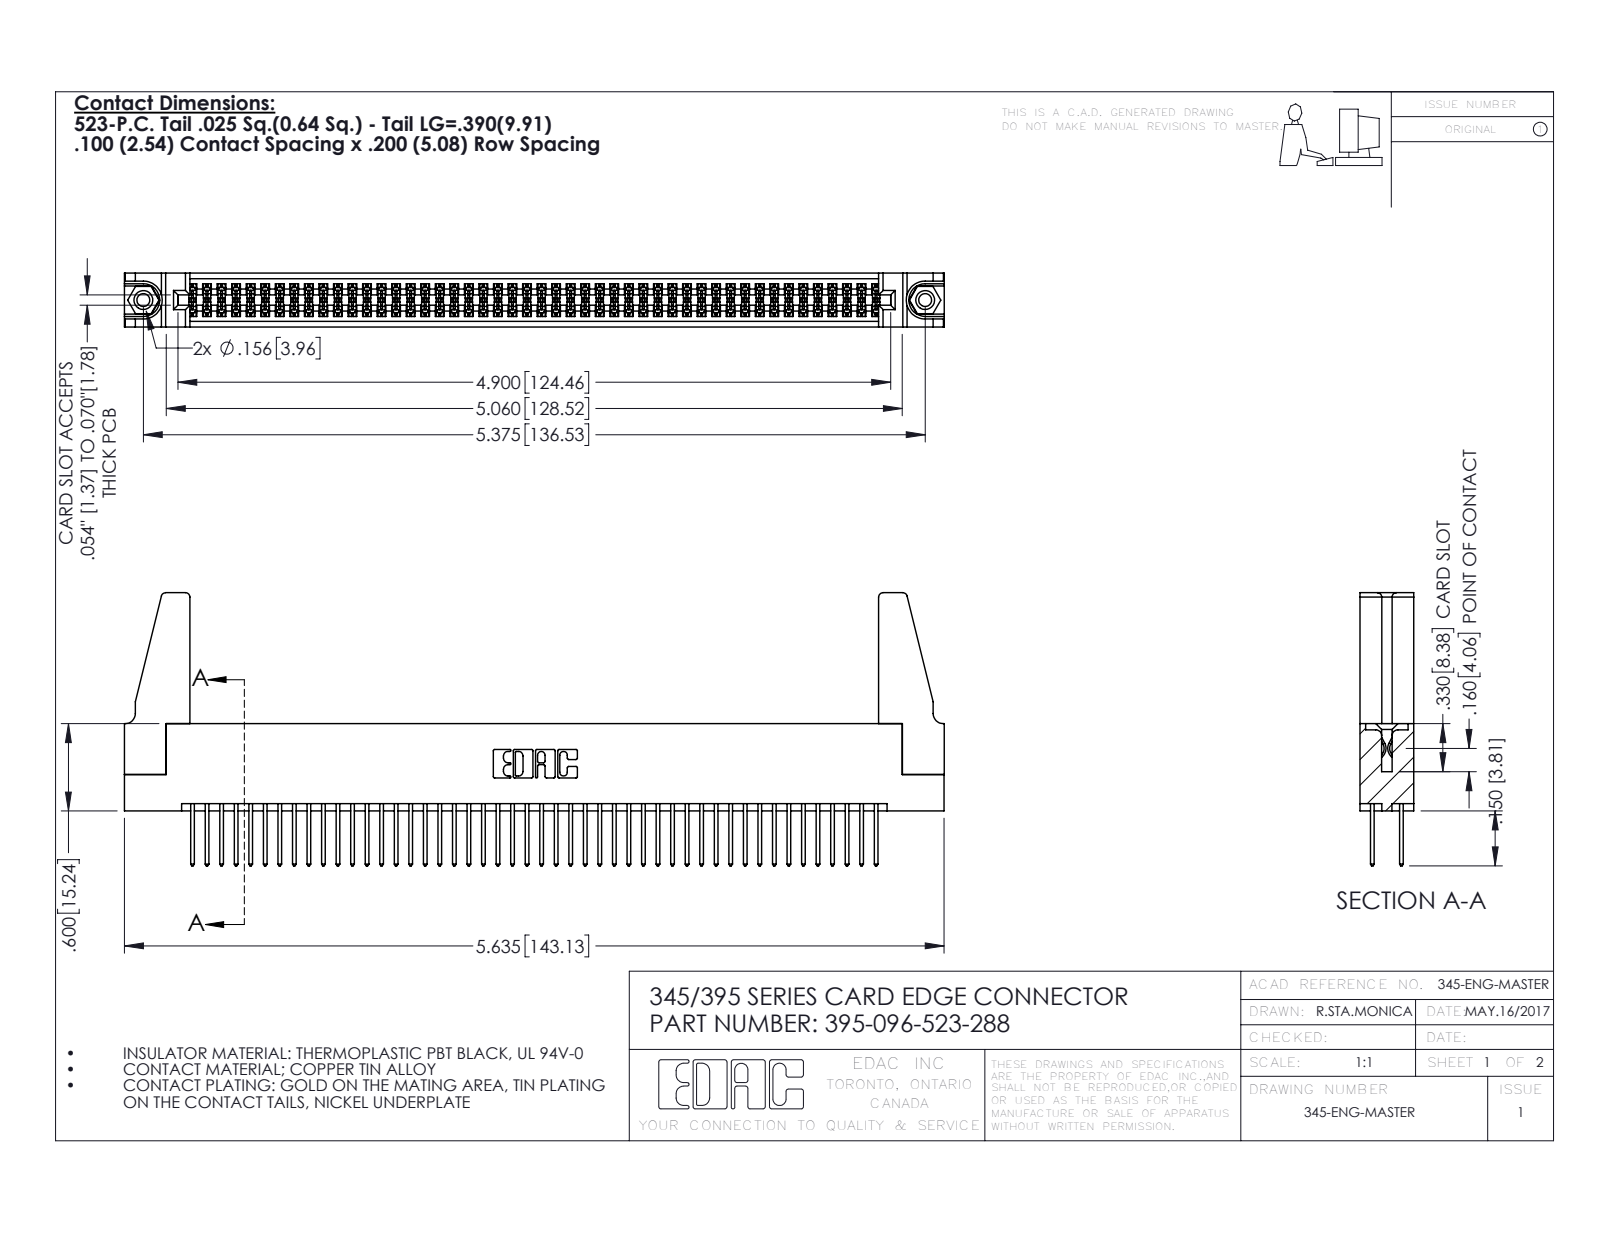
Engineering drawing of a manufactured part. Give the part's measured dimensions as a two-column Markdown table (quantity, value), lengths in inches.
| quantity | value |
| --- | --- |
| part name | 345-250-001_345-250-001-102; 395-096-523-288; 345-220-078_345-220-088; 345-292-001_345-293-123 (+1 more) |
| STEP written by | SolidWorks 2016 (CONFIG_CONTROL_DESIGN) |
| units | inches |
| bodies | 101 solids, 5050 faces (3320 planar, 1714 cylindrical, 16 other) |
| overall size | 5.636 × 1.877 × 0.37 |
| volume | 1.062 in³ |
| surface area | 38.83 in² |
| round holes (diameter × count) | 0.089 × 2, 0.125 × 2, 0.156 × 2, 0.064 × 1 |
| round bosses / shafts (diameter × count) | 0.155 × 2 |
| partial cylindrical surfaces (radius × count) | 0.006 × 144, 0.01 × 96, 0.01 × 22, 0.03 × 8, 0.007 × 6, 0.031 × 6, 0.026 × 3, 0.014 × 2 |
| main face-to-face distances | 0.072, 0.298, 0.2, 0.37, 0.098, 0.272, 0.025, 0.225, 0.175, 0.149 |
| hole center spacings | 0.27, 5.139, 5.375 |
